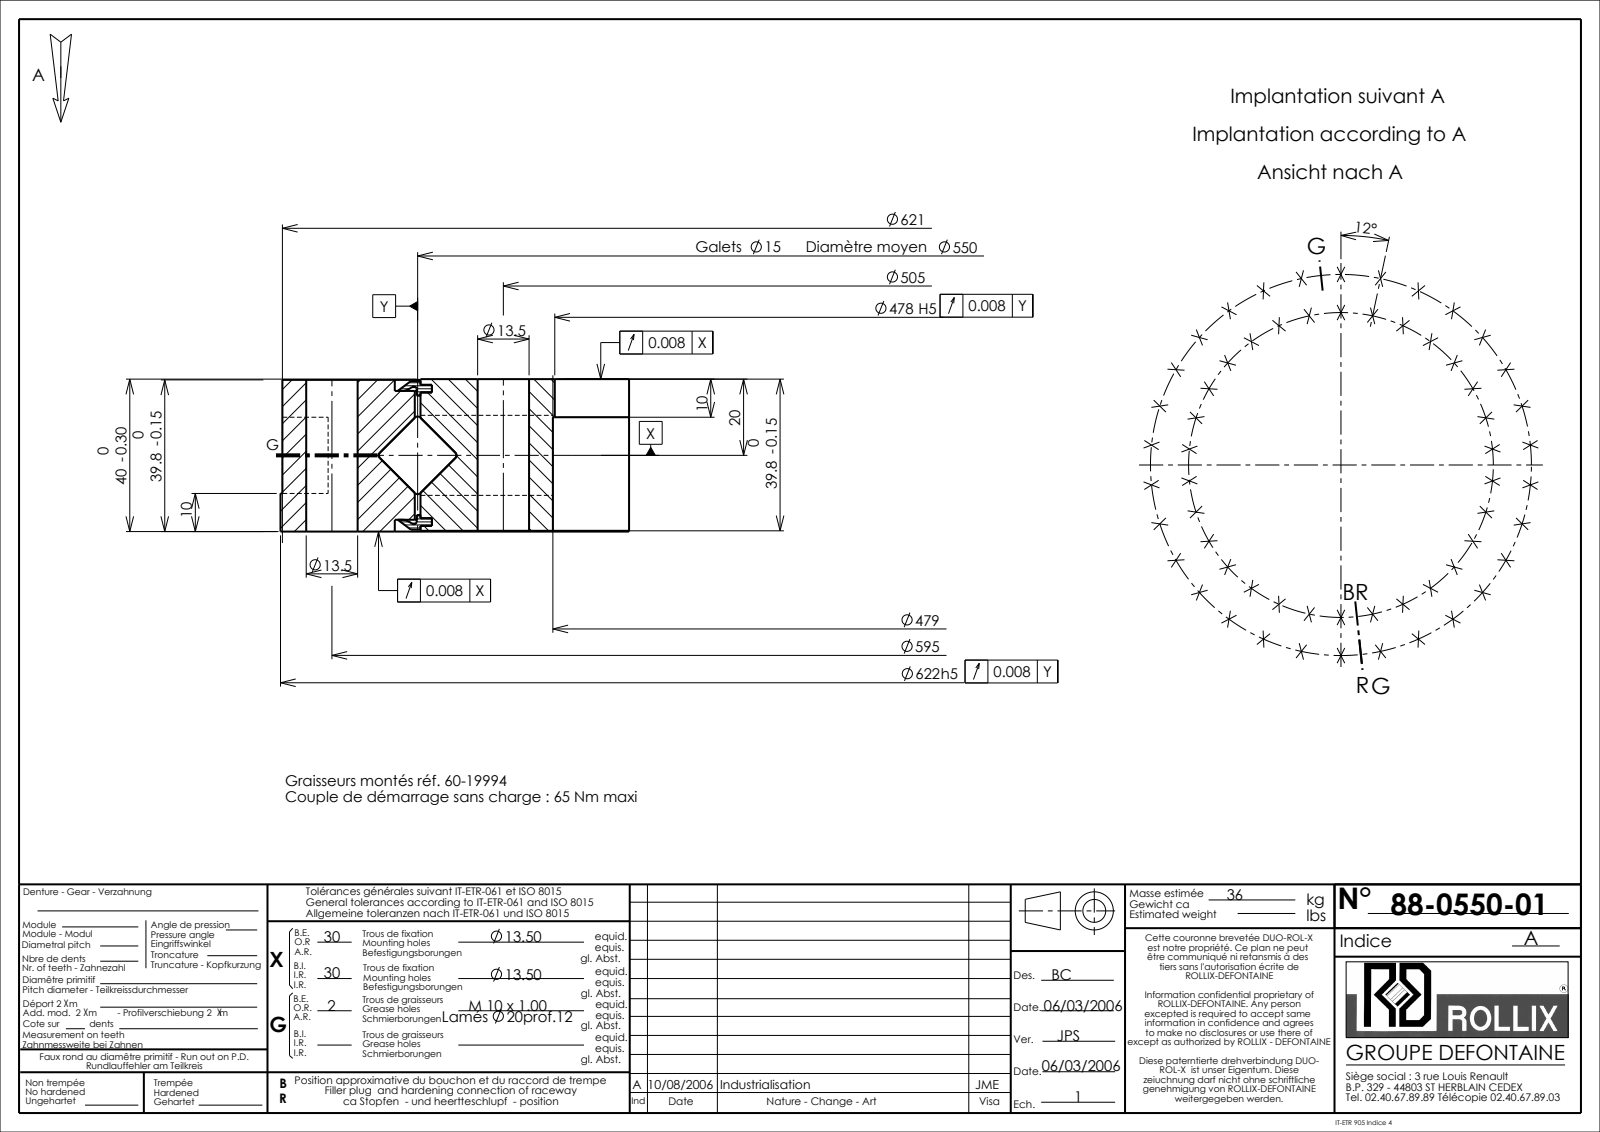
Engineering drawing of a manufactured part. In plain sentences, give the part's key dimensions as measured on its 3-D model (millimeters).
The part is named "88-0550-01". Its 3-D file was written by "SolidWorks 2016 (CONFIG_CONTROL_DESIGN)". It is 7 solids with 279 faces: 46 planar, 178 cylindrical and 55 other. Overall it measures 622 by 622 by 40 millimeters. Its volume is 4 093 000 cubic millimeters and its surface area 739 187 square millimeters. Round holes: 60 of diameter 13.5, 2 of diameter 9, 2 of diameter 20, 1 of diameter 478, 1 of diameter 479, 1 of diameter 542.5, 1 of diameter 548.5, 1 of diameter 551.5, 1 of diameter 562. Round bosses or shafts: 2 of diameter 10, 1 of diameter 622, 1 of diameter 621, 1 of diameter 550.5, 1 of diameter 15. The main face-to-face distances are 39.8, 39.6, 40, 3.1, 36.9, 2.9, 36.7, 3.5, 36.5, 3.3. The hole center spacings are 543.56, 582, 442.17, 297.5, 591.74, 242.01, 565.88, 62.19.
